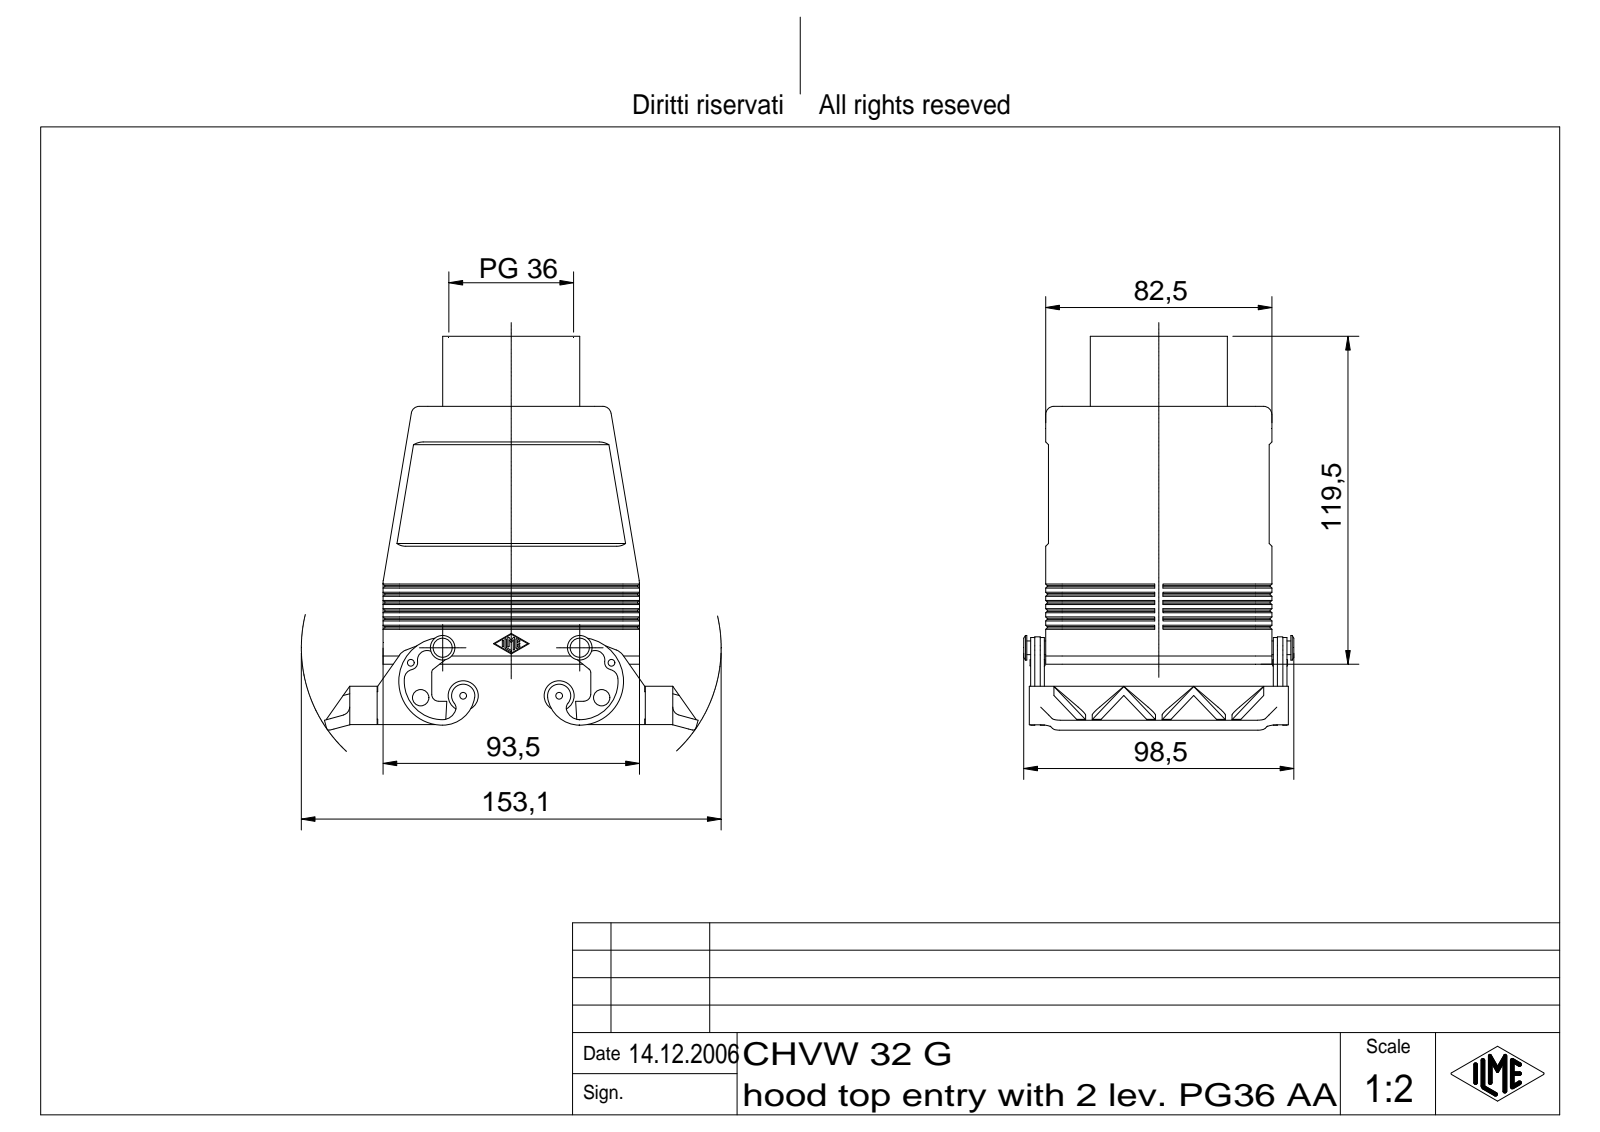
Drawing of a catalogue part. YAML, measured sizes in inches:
part_name: "CHVW 32 G"
step_written_by: "Autodesk Inventor 7 (AUTOMOTIVE_DESIGN)"
units: inches
bodies: {solids: 1, faces: 1080, planar: 325, cylindrical: 292, other: 463}
overall_size: [5.651, 5.365, 3.878]
volume: 11.32
surface_area: 158.9
round_holes:
  - {diameter: 0.097, count: 4}
  - {diameter: 0.138, count: 4}
  - {diameter: 0.098, count: 2}
  - {diameter: 0.236, count: 2}
  - {diameter: 1.712, count: 1}
  - {diameter: 1.791, count: 1}
round_bosses_or_shafts:
  - {diameter: 0.433, count: 2}
  - {diameter: 0.354, count: 2}
  - {diameter: 0.197, count: 2}
  - {diameter: 0.079, count: 2}
  - {diameter: 2.559, count: 1}
  - {diameter: 2.323, count: 1}
  - {diameter: 1.969, count: 1}
partial_cylinders:
  - {radius: 0.01, count: 14}
  - {radius: 0.118, count: 14}
  - {radius: 0.079, count: 12}
  - {radius: 0.236, count: 10}
  - {radius: 0.039, count: 6}
  - {radius: 0.098, count: 6}
  - {radius: 0.138, count: 4}
  - {radius: 0.197, count: 4}
face_to_face_distances: [0.157, 3.248, 3.091, 2.933, 0.118, 0.039, 2.815, 0.433, 3.051, 3.209]
hole_center_spacings: [0.52, 1.063, 1.534, 1.954, 2.785, 3.051, 3.231, 2.598]
